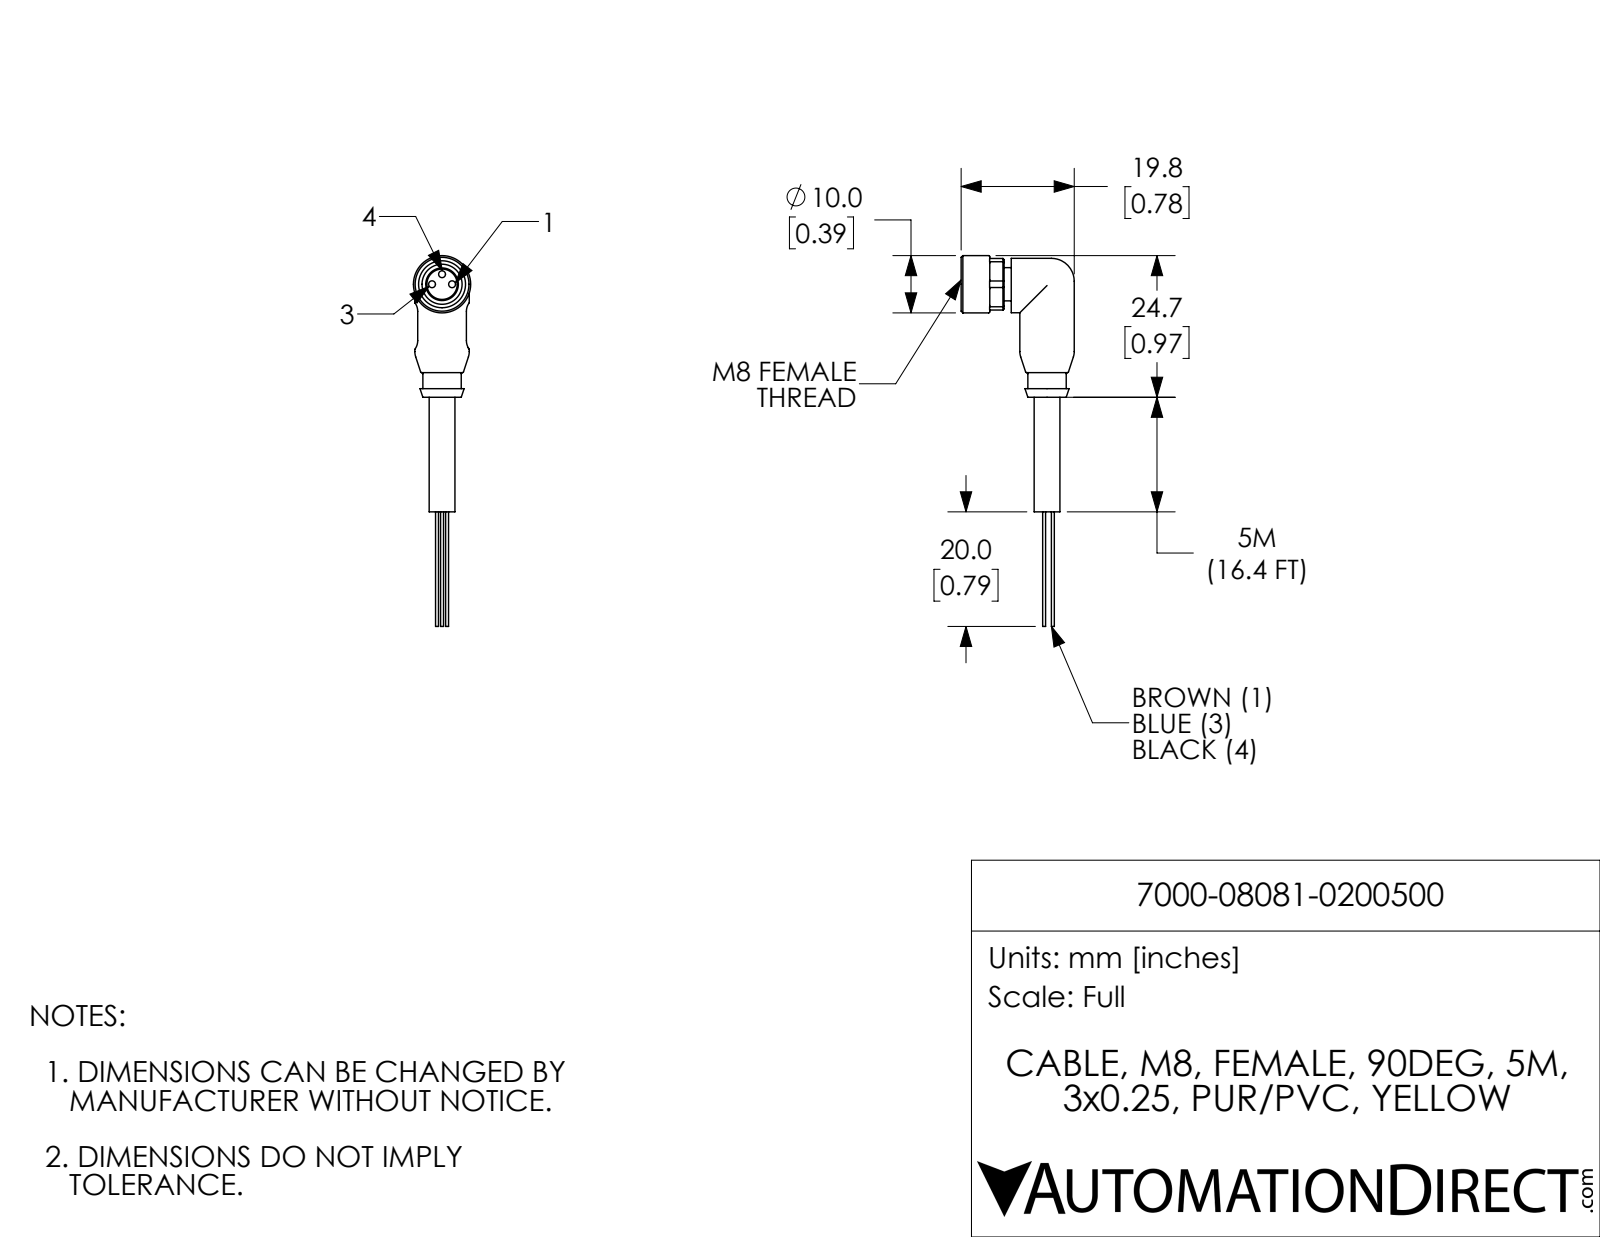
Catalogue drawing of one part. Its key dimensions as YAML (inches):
part_name: "7000-08081-0200500"
step_written_by: "SolidWorks 2017 (AUTOMOTIVE_DESIGN)"
units: inches
bodies: {solids: 1, faces: 107, planar: 35, cylindrical: 43, other: 29}
overall_size: [2.548, 0.778, 0.394]
volume: 0.147
surface_area: 2.844
round_holes:
  - {diameter: 0.047, count: 3}
  - {diameter: 0.276, count: 1}
round_bosses_or_shafts:
  - {diameter: 0.02, count: 3}
  - {diameter: 0.374, count: 2}
  - {diameter: 0.394, count: 1}
  - {diameter: 0.264, count: 1}
  - {diameter: 0.228, count: 1}
  - {diameter: 0.224, count: 1}
  - {diameter: 0.177, count: 1}
partial_cylinders:
  - {radius: 0.008, count: 4}
  - {radius: 0.098, count: 4}
  - {radius: 0.193, count: 1}
face_to_face_distances: [0.049, 0.354, 0.059, 0.335, 0.028, 0.268, 0.317, 0.295, 0.344, 0.787]
hole_center_spacings: [0.069, 0.097, 0.138]
